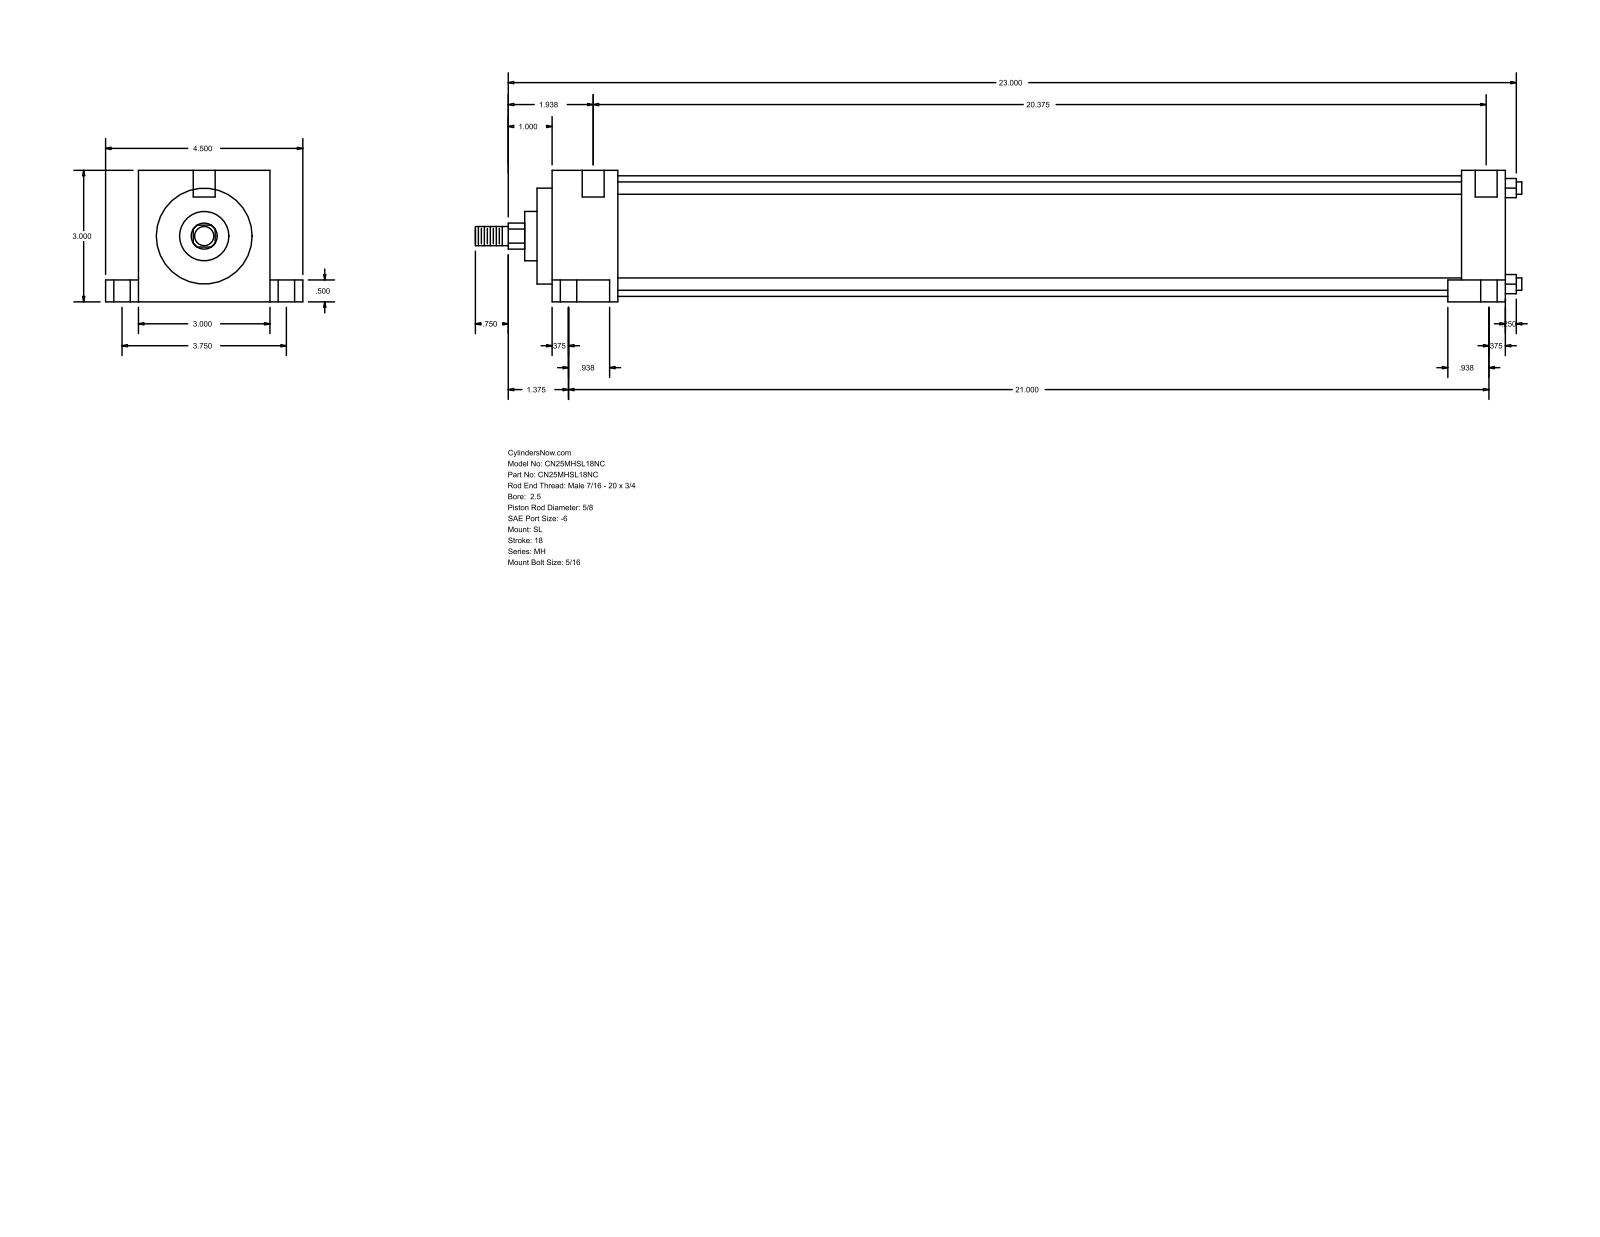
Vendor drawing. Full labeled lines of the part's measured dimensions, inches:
Part name (STEP PRODUCT): MH_SL__0250_0.625
STEP written by: GSSL Pune (CONFIG_CONTROL_DESIGN)
Units: inches
Bodies: 0 solids, 86 faces (61 planar, 25 cylindrical, 0 other)
Overall size (bounding box): 23.875 × 4.5 × 3
Round holes (diameter × count): ⌀0.219 ×2, ⌀0.375 ×2, ⌀0.625 ×2, ⌀0.5 ×1
Round bosses / shafts (diameter × count): ⌀0.281 ×4, ⌀2.75 ×1, ⌀2.187 ×1, ⌀1.125 ×1, ⌀0.625 ×1, ⌀0.437 ×1
Partial cylindrical surfaces — rounded edges, fillets, slot ends (radius × count): R0.297 ×1
Main face-to-face distances: 3, 1, 21.094, 22.094, 2.5, 0.5, 0.75, 3.75, 1.25, 20.781
Hole centre spacings: 1.876, 0.125, 3.75
